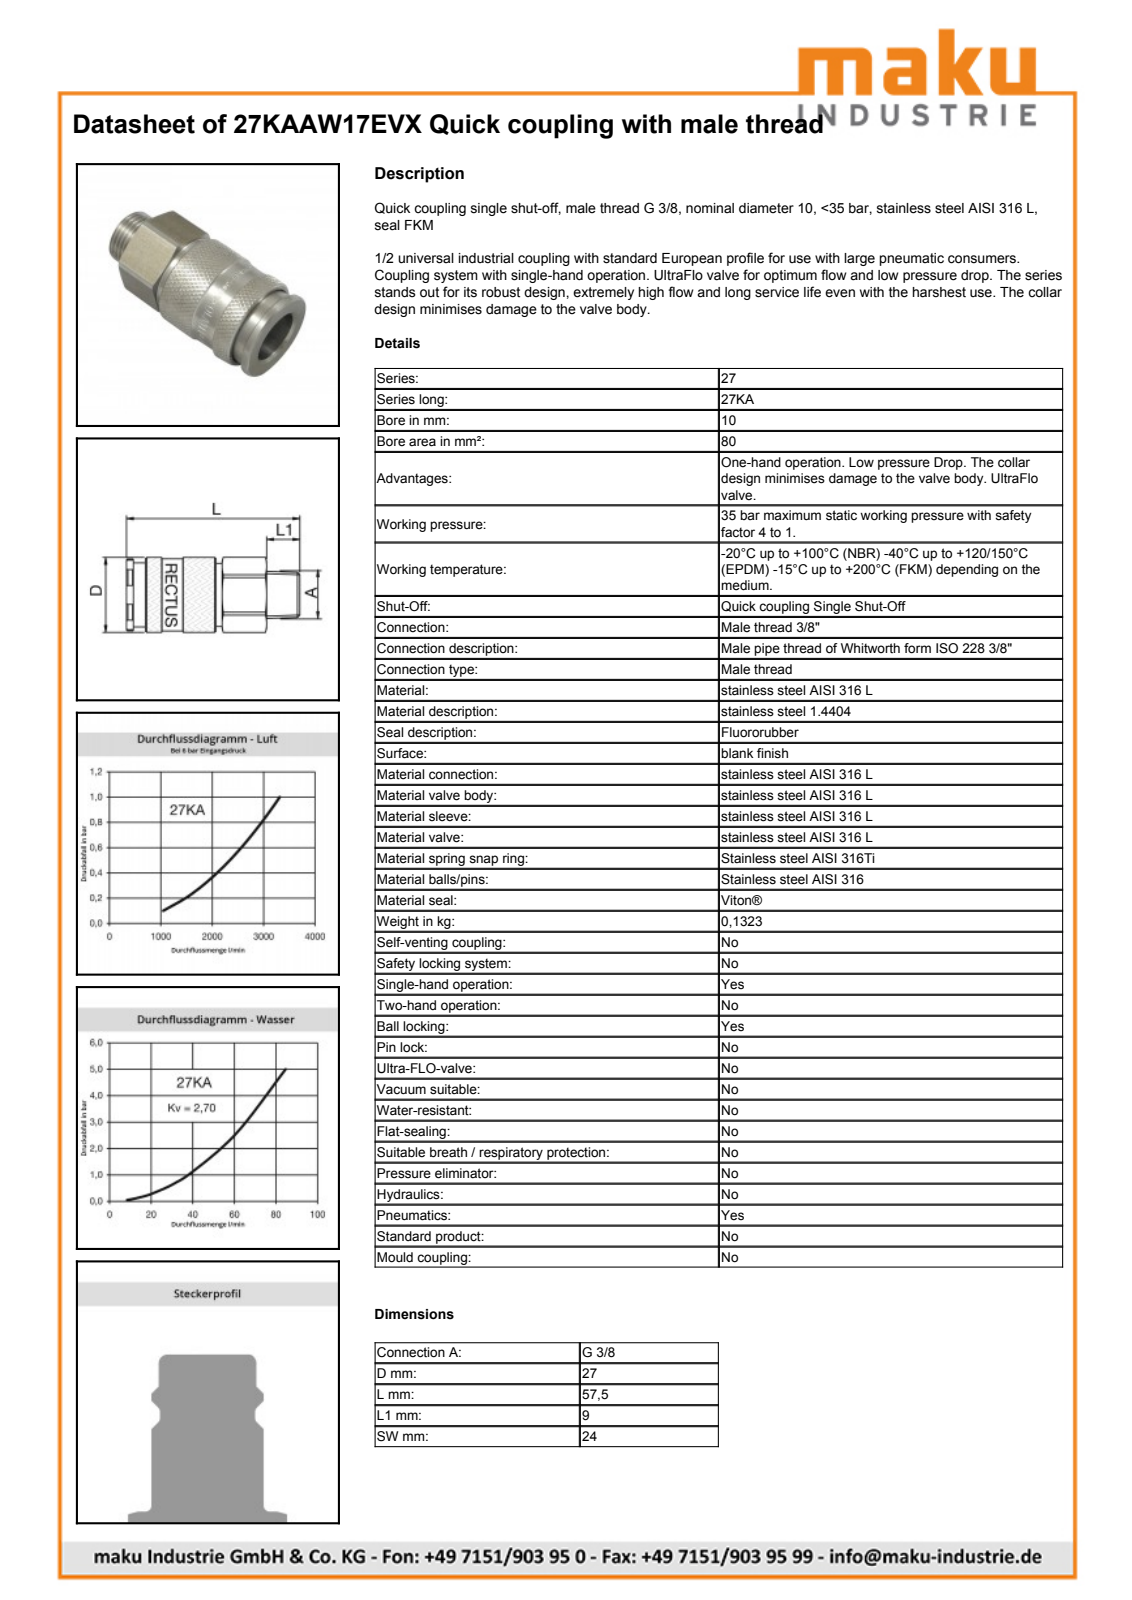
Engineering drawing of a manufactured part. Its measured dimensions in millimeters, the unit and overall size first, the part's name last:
Units: millimetres
Overall size (bounding box): 57.45 × 27.15 × 27.15
Round holes (diameter × count): ⌀20.3 ×1, ⌀20.95 ×1, ⌀23.35 ×1, ⌀23.55 ×1
Round bosses / shafts (diameter × count): ⌀27.15 ×1, ⌀26 ×1, ⌀23.1 ×1, ⌀22.8 ×1, ⌀20 ×1, ⌀16.66 ×1
Partial cylindrical surfaces — rounded edges, fillets, slot ends (radius × count): R9.61 ×1, R12.9 ×1, R13.53 ×1
Main face-to-face distances: 24, 48.45, 57.45, 9, 32.3, 16.15, 25.15, 6.8, 25.5, 41.65
Volume: 25 205 mm³ · Surface area: 9 829 mm²
Bodies: 2 solids, 825 faces (320 planar, 87 cylindrical, 418 other)
Part name (STEP PRODUCT): D106660
STEP written by: Autodesk Inventor 2011 (AUTOMOTIVE_DESIGN)
